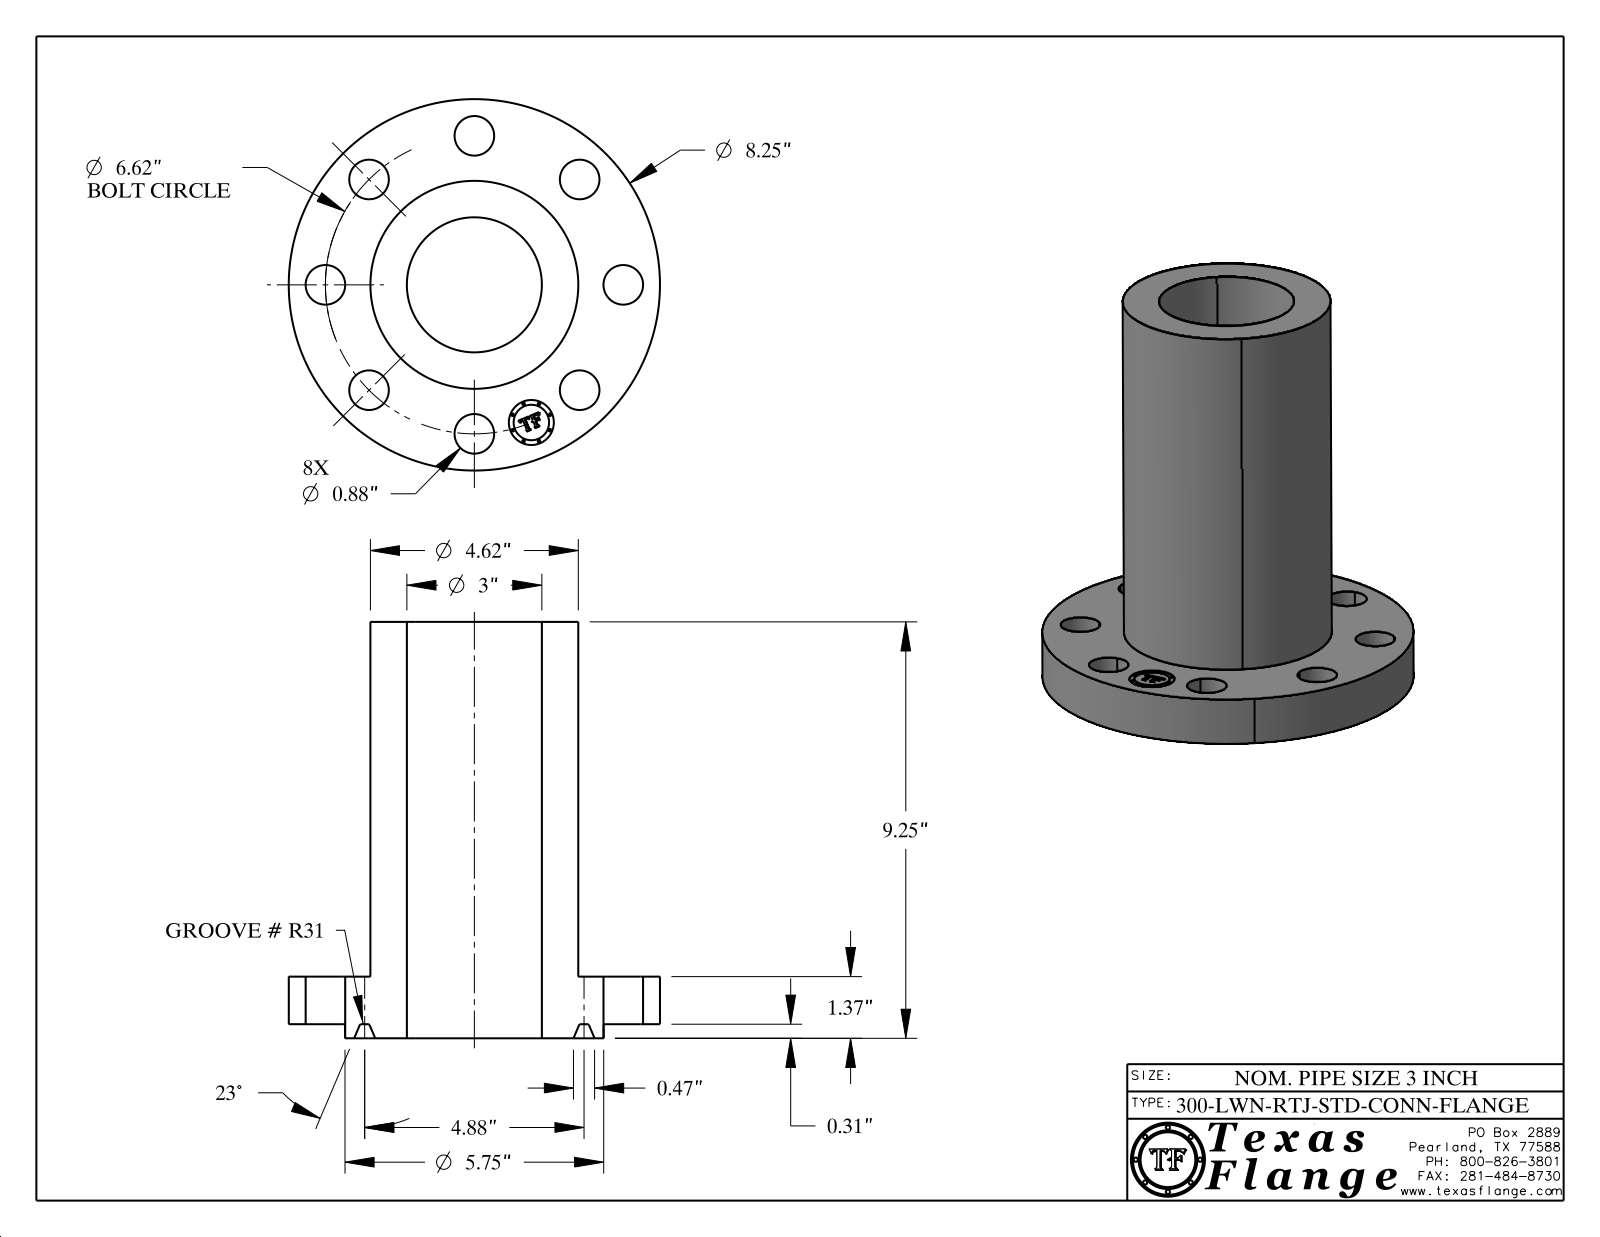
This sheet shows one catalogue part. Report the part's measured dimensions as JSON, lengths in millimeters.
{"part_name": "3-300-LWN-RTJ-STD-CONN-FLANGE", "step_written_by": "CATIA V5 STEP AP214 (AUTOMOTIVE_DESIGN)", "units": "millimeters", "bodies": {"solids": 1, "faces": 431, "planar": 371, "cylindrical": 52, "other": 8}, "overall_size": [235, 209.6, 209.6], "volume_mm3": 2042000, "surface_area_mm2": 224100, "round_holes": [[22.4, 8], [25.4, 1], [76.2, 1]], "round_bosses_or_shafts": [[1.5, 8], [209.6, 1], [146.1, 1], [117.3, 1], [20, 1]], "face_to_face_distances": [26.8, 8, 34.8, 235, 227, 200.2, 34.7, 26.7, 200.3, 7.6], "hole_center_spacings": [84.1, 64.3, 155.3, 118.9, 118.9, 32.8, 93.4, 164.9]}
